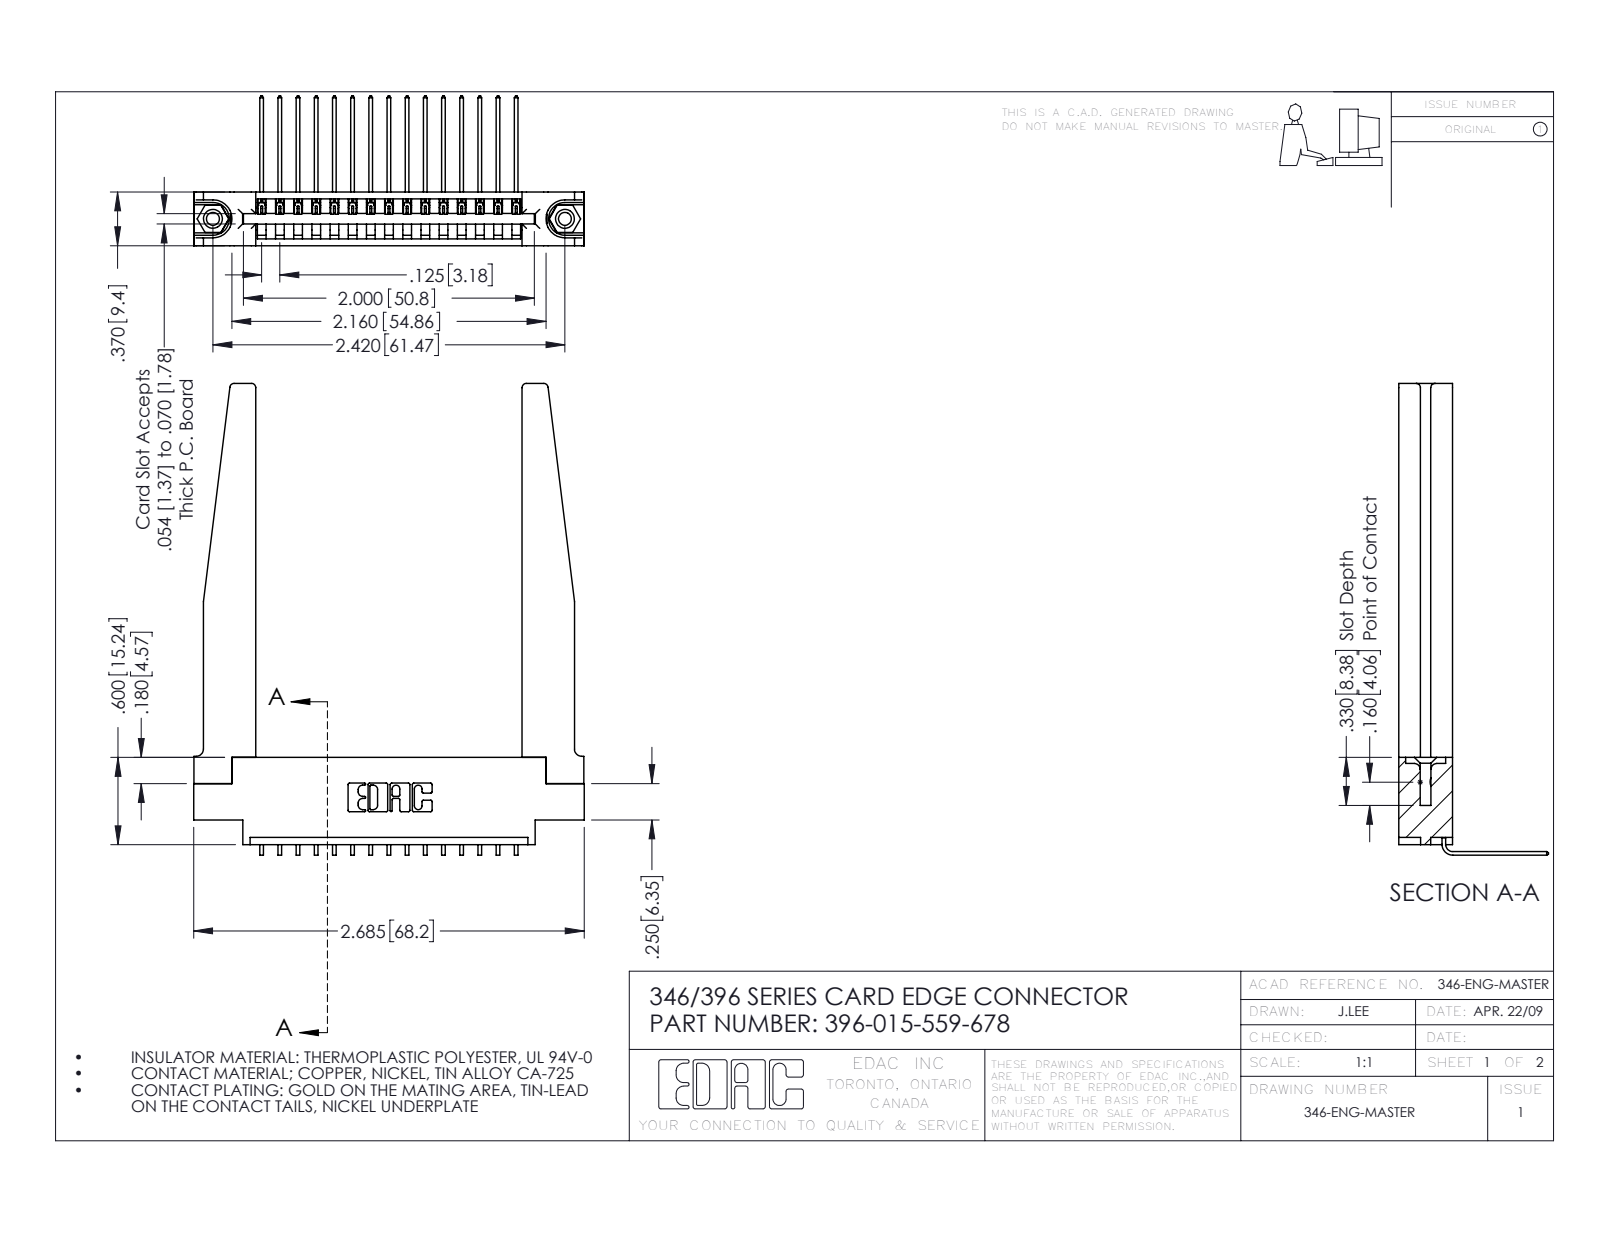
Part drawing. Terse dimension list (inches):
name: 345-292-001_558 559 Tail - 1; 346-220-078_345-220-078; 346 Part_0.170 Offset - 0.156 Dia-TH; 345-250-001_345-250-001-102 (+1 more)
written by: SolidWorks 2016 (CONFIG_CONTROL_DESIGN)
unit: in
bodies: 20 solids, 1260 faces (852 planar, 356 cylindrical, 52 other)
size: 3.243 × 2.685 × 1.03
volume: 0.802 in³; area: 22.48 in²
holes: 2× ⌀0.089, 2× ⌀0.125, 2× ⌀0.156, 1× ⌀0.064
bosses: 2× ⌀0.155
rounds: 30× R0.006, 22× R0.01, 8× R0.03, 6× R0.007, 6× R0.031, 3× R0.026, 3× R0.05, 2× R0.031
face distances: 0.37, 0.072, 0.15, 0.048, 0.148, 0.322, 0.25, 0.025, 0.102, 0.22
hole spacings: 0.246, 2.213, 2.42
